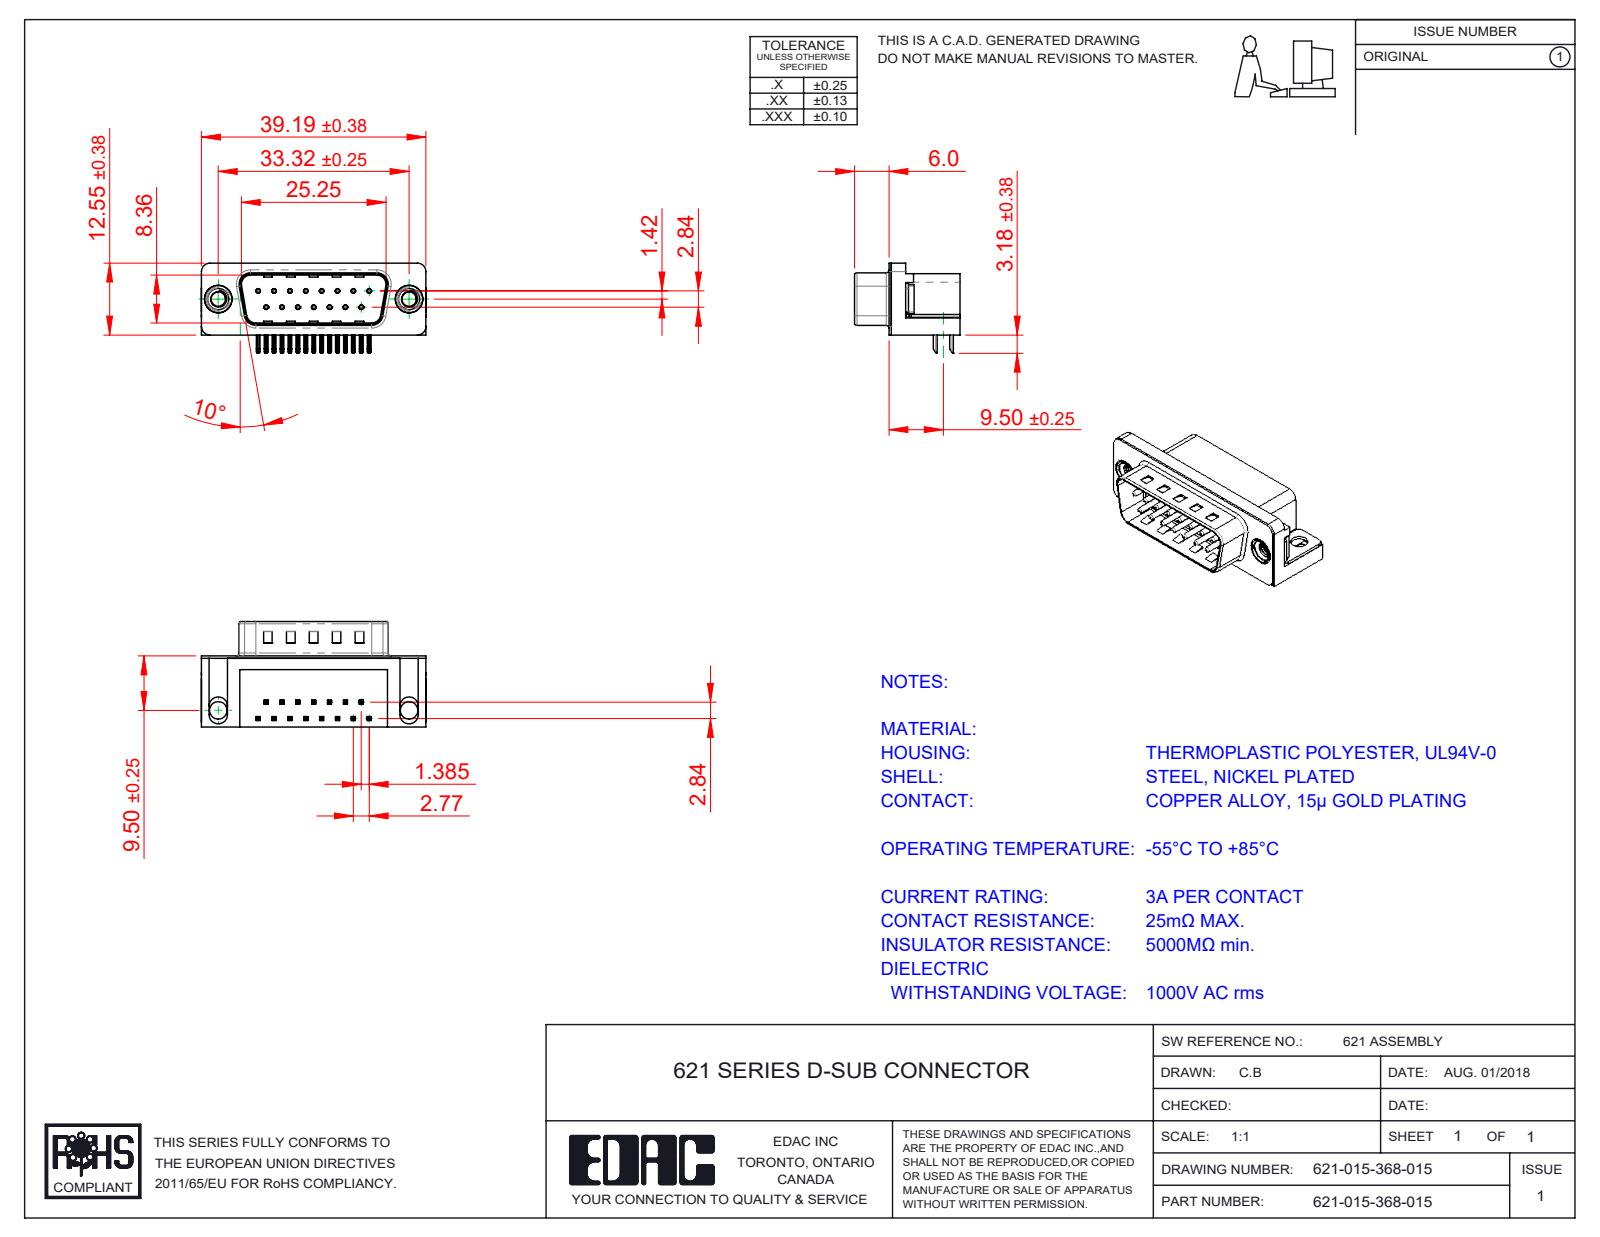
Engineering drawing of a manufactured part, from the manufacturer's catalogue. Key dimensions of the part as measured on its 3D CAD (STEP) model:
Part name (STEP PRODUCT): 621 M3 Threaded Rivet; 621 Contact Top; 621 Housing_15 Socket; 621 Thru Hole Board Mount (+3 more)
STEP written by: SolidWorks 2016 (CONFIG_CONTROL_DESIGN)
Units: millimetres
Bodies: 21 solids, 1475 faces (891 planar, 449 cylindrical, 135 other)
Overall size (bounding box): 39.22 × 18.4 × 15.73
Volume: 4 408 mm³ · Surface area: 5 640 mm²
Round holes (diameter × count): ⌀0.35 ×15, ⌀0.8 ×15, ⌀2.5 ×2, ⌀3.05 ×2, ⌀4 ×2, ⌀4.8 ×2, ⌀5 ×2
Round bosses / shafts (diameter × count): ⌀0.75 ×15, ⌀4.9 ×2, ⌀4.75 ×2, ⌀3.9 ×2
Partial cylindrical surfaces — rounded edges, fillets, slot ends (radius × count): R0.25 ×68, R0.12 ×30, R1 ×16, R0.5 ×9, R1.6 ×8, R1.5 ×6, R0.9 ×4, R2 ×4
Main face-to-face distances: 0.4, 12, 10.35, 2.1, 10.46, 12.4, 1.7, 10.86, 8.76, 2.9
Hole centre spacings: 3.16, 2.77, 5.54, 8.31, 11.08, 5.03, 5.04, 7.48
